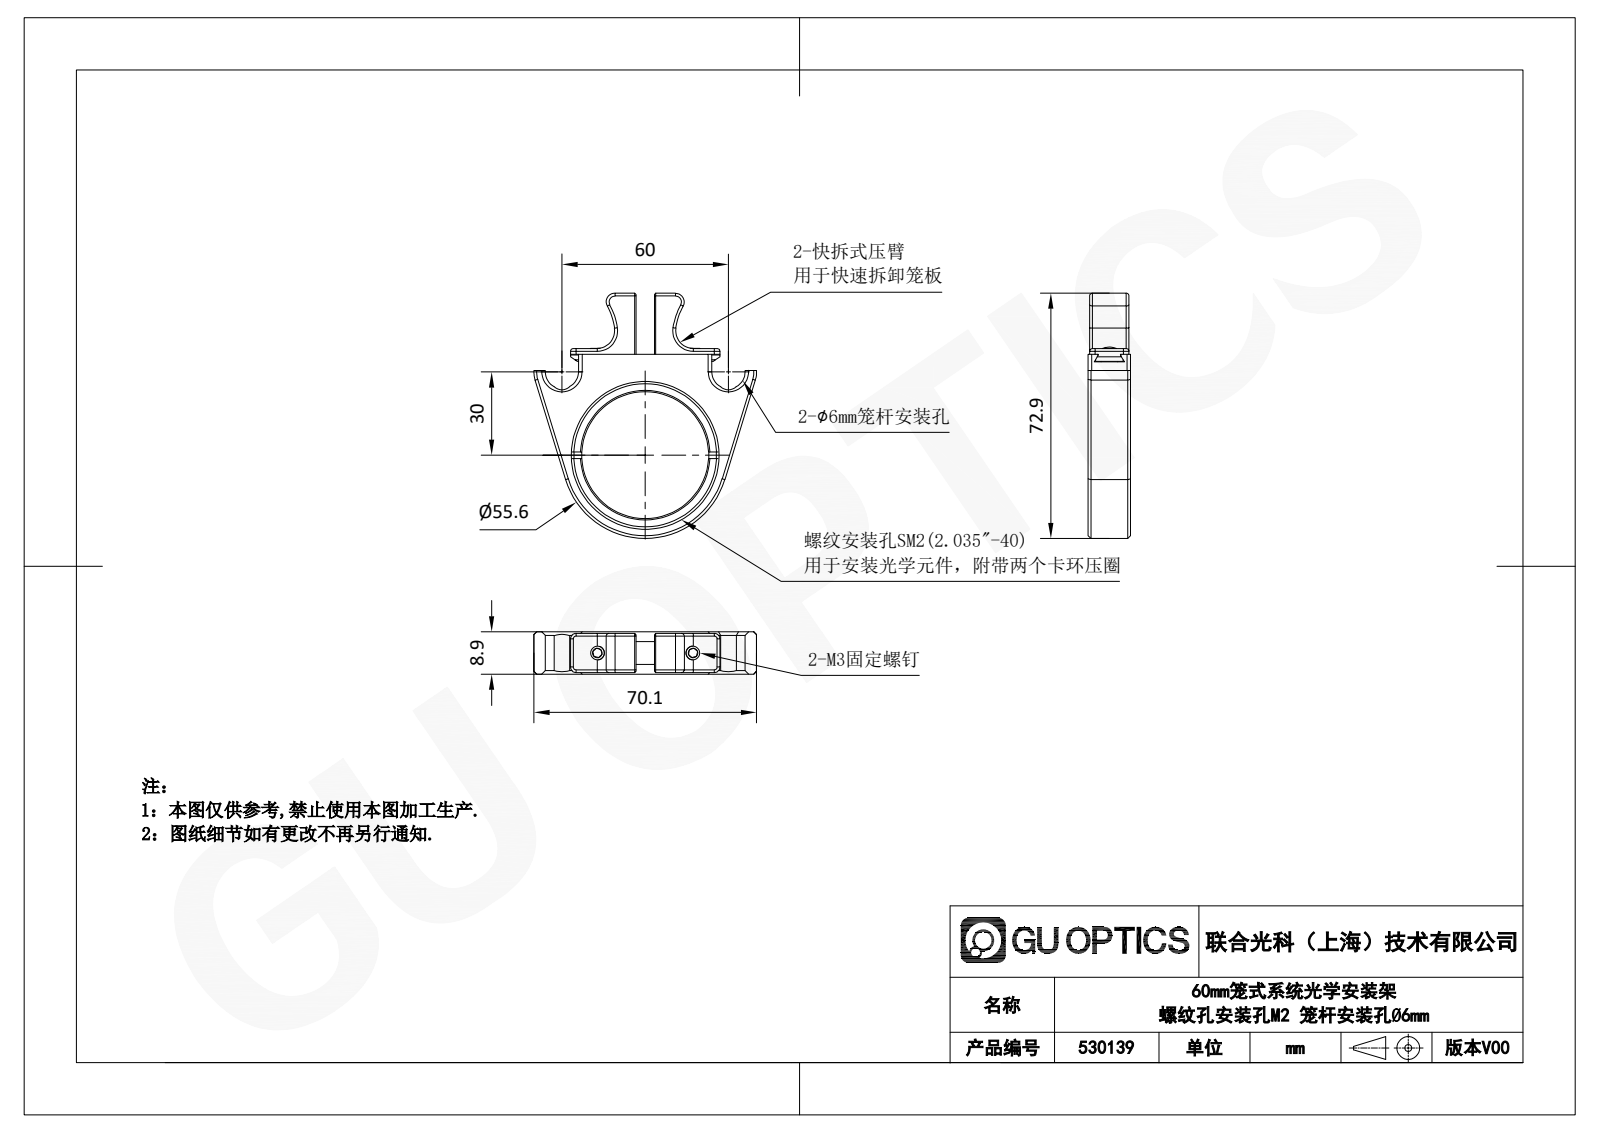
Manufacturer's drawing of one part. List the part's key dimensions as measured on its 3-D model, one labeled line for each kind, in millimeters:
Part name (STEP PRODUCT): 530139
STEP written by: SolidWorks 2020 (CONFIG_CONTROL_DESIGN)
Units: millimetres
Bodies: 0 solids, 189 faces (101 planar, 44 cylindrical, 44 other)
Overall size (bounding box): 72.93 × 70.1 × 8.89
Round holes (diameter × count): ⌀2.5 ×2, ⌀3.18 ×2, ⌀48.3 ×1, ⌀51.05 ×1
Round bosses / shafts (diameter × count): ⌀3 ×2, ⌀51.69 ×1
Partial cylindrical surfaces — rounded edges, fillets, slot ends (radius × count): R0.8 ×6, R1.5 ×4, R1.5 ×4, R1.57 ×2, R1.98 ×2, R3.01 ×2, R3.17 ×2, R12.7 ×2
Main face-to-face distances: 8.89, 2.5, 6.39, 1.74, 1.9, 1.46, 1.62, 3.38, 3.1, 1.64
Hole centre spacings: 5.21, 46.68
